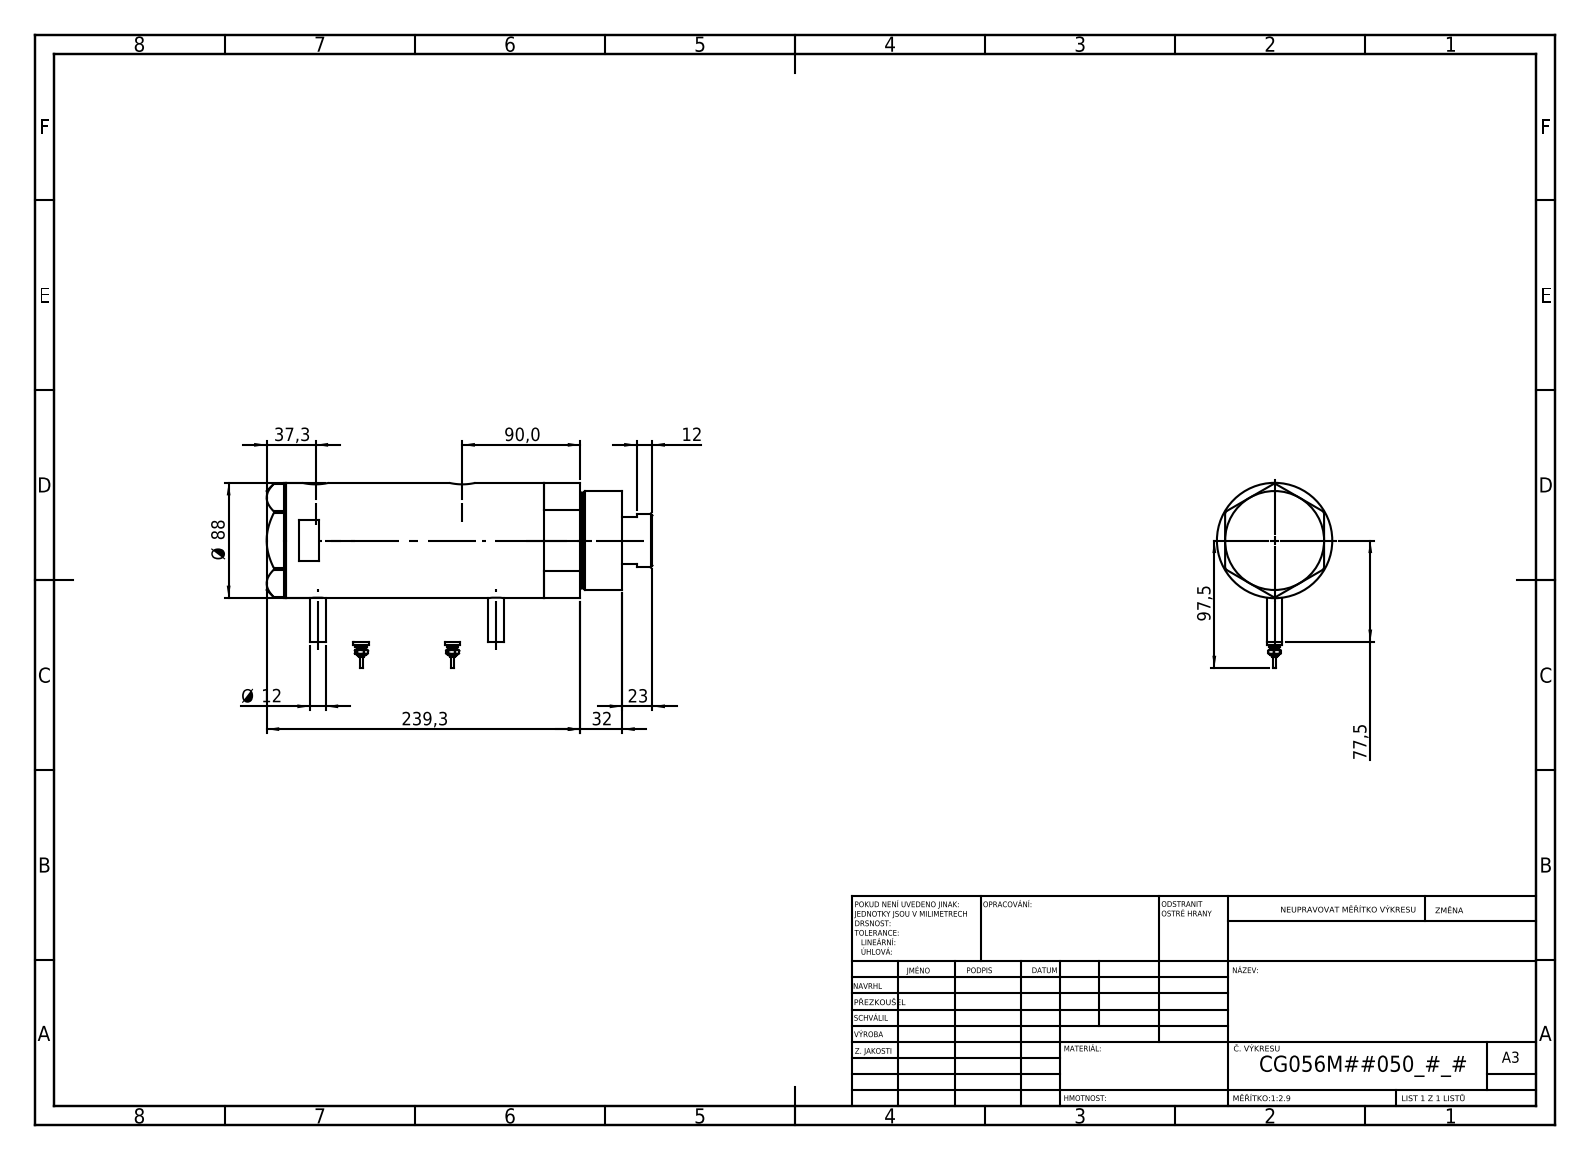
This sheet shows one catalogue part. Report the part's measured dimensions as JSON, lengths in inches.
{"part_name": "V270CG_BACK; V270CG_FRONT; V270CG_VC; V270CG_MIDDLE (+1 more)", "step_written_by": "SolidWorks 2019 (CONFIG_CONTROL_DESIGN)", "units": "inches", "bodies": {"solids": 6, "faces": 213, "planar": 80, "cylindrical": 69, "other": 64}, "overall_size": [11.587, 5.571, 3.465], "volume_in3": 94.04, "surface_area_in2": 348.1, "round_holes": [[0.492, 2], [0.518, 2], [0.787, 2], [0.571, 1], [1.654, 1], [1.713, 1], [2.205, 1], [2.362, 1], [3.15, 1]], "round_bosses_or_shafts": [[0.472, 4], [0.354, 2], [0.276, 2], [0.177, 2], [0.098, 2], [3.465, 1], [2.953, 1], [2.874, 1]], "face_to_face_distances": [5.291, 1.024, 4.268, 0.591, 1.614, 5.882, 10.091, 10.681, 9.067, 4.799], "hole_center_spacings": [0.067, 1.016, 4.343, 4.409, 5.358, 5.425]}
